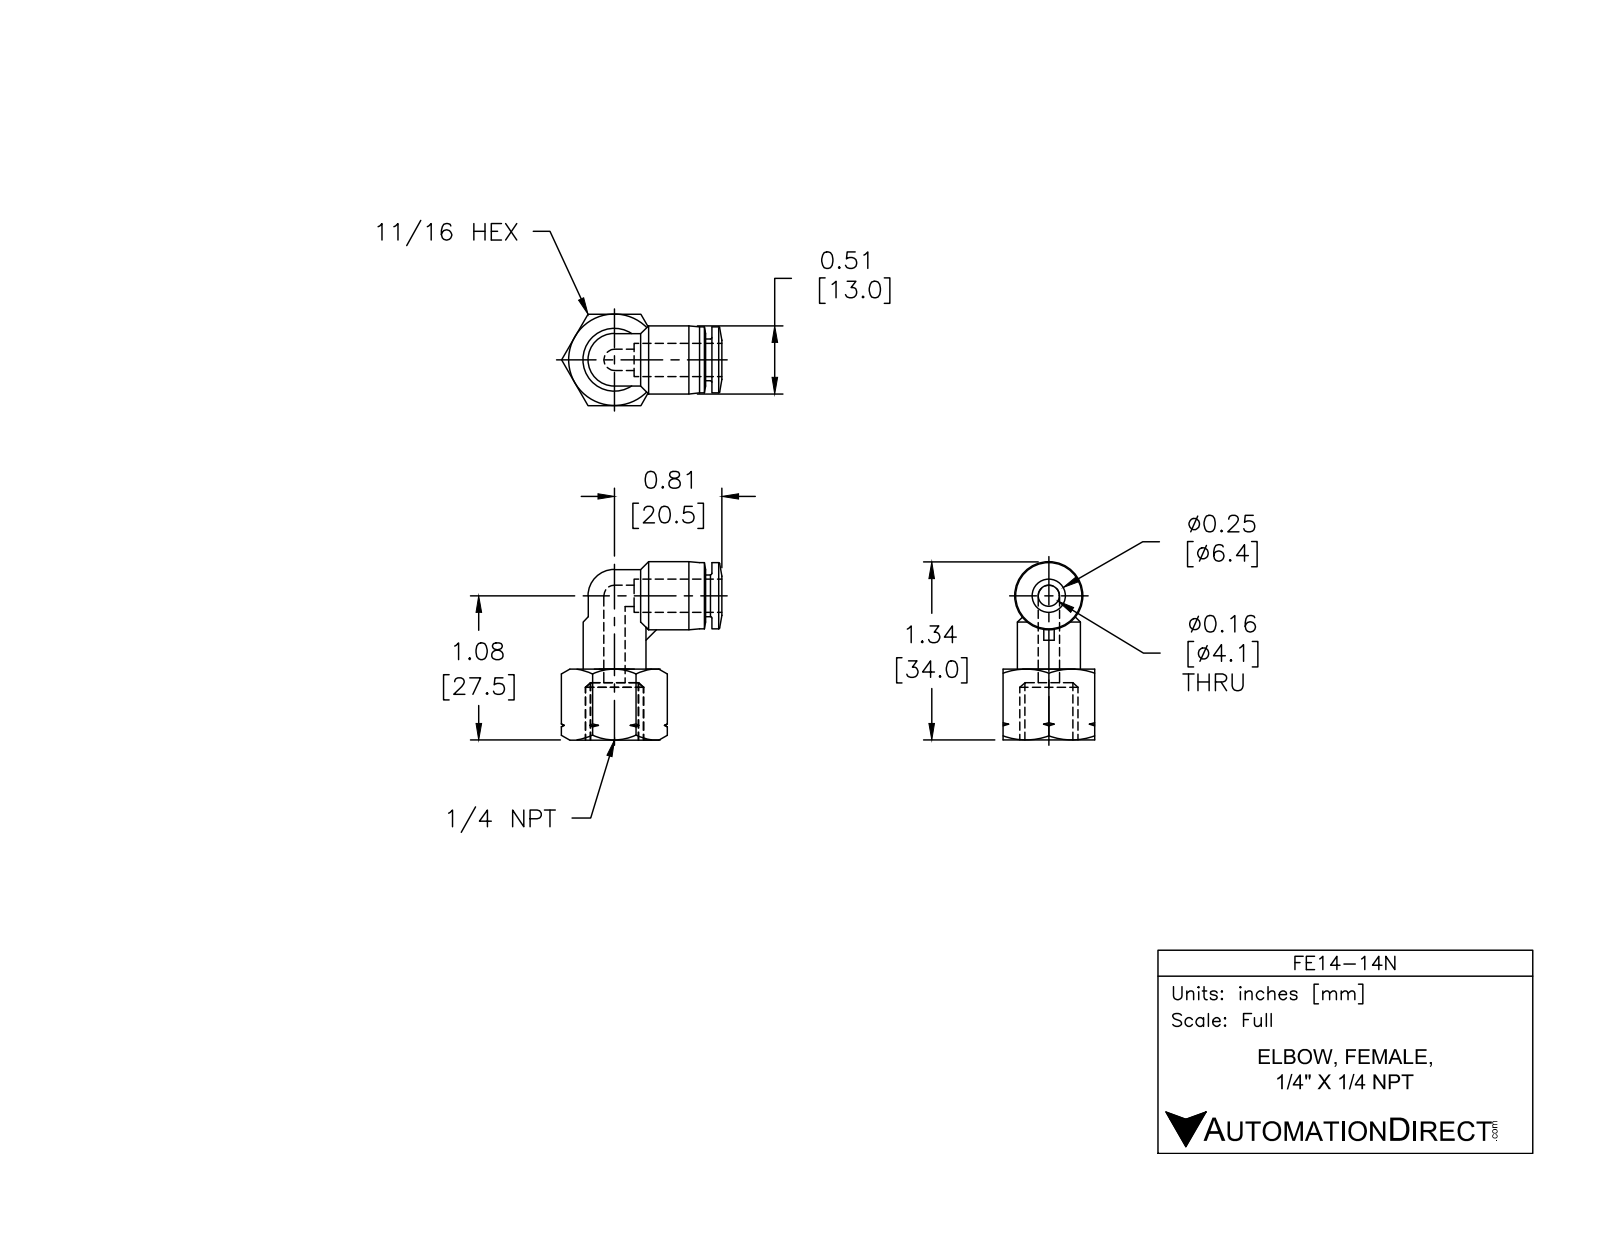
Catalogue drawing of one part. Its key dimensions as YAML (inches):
part_name: "FE14-14N"
step_written_by: "SolidWorks 2015 (AUTOMOTIVE_DESIGN)"
units: inches
bodies: {solids: 1, faces: 86, planar: 15, cylindrical: 20, other: 51}
overall_size: [1.339, 1.204, 0.687]
volume: 0.295
surface_area: 5.781
round_holes:
  - {diameter: 0.157, count: 2}
  - {diameter: 0.258, count: 1}
round_bosses_or_shafts:
  - {diameter: 0.394, count: 2}
  - {diameter: 0.512, count: 1}
  - {diameter: 0.496, count: 1}
  - {diameter: 0.472, count: 1}
  - {diameter: 0.313, count: 1}
face_to_face_distances: [0.687, 0.098, 0.433, 0.531, 0.047, 0.539, 0.587, 0.304, 0.383, 0.079]
